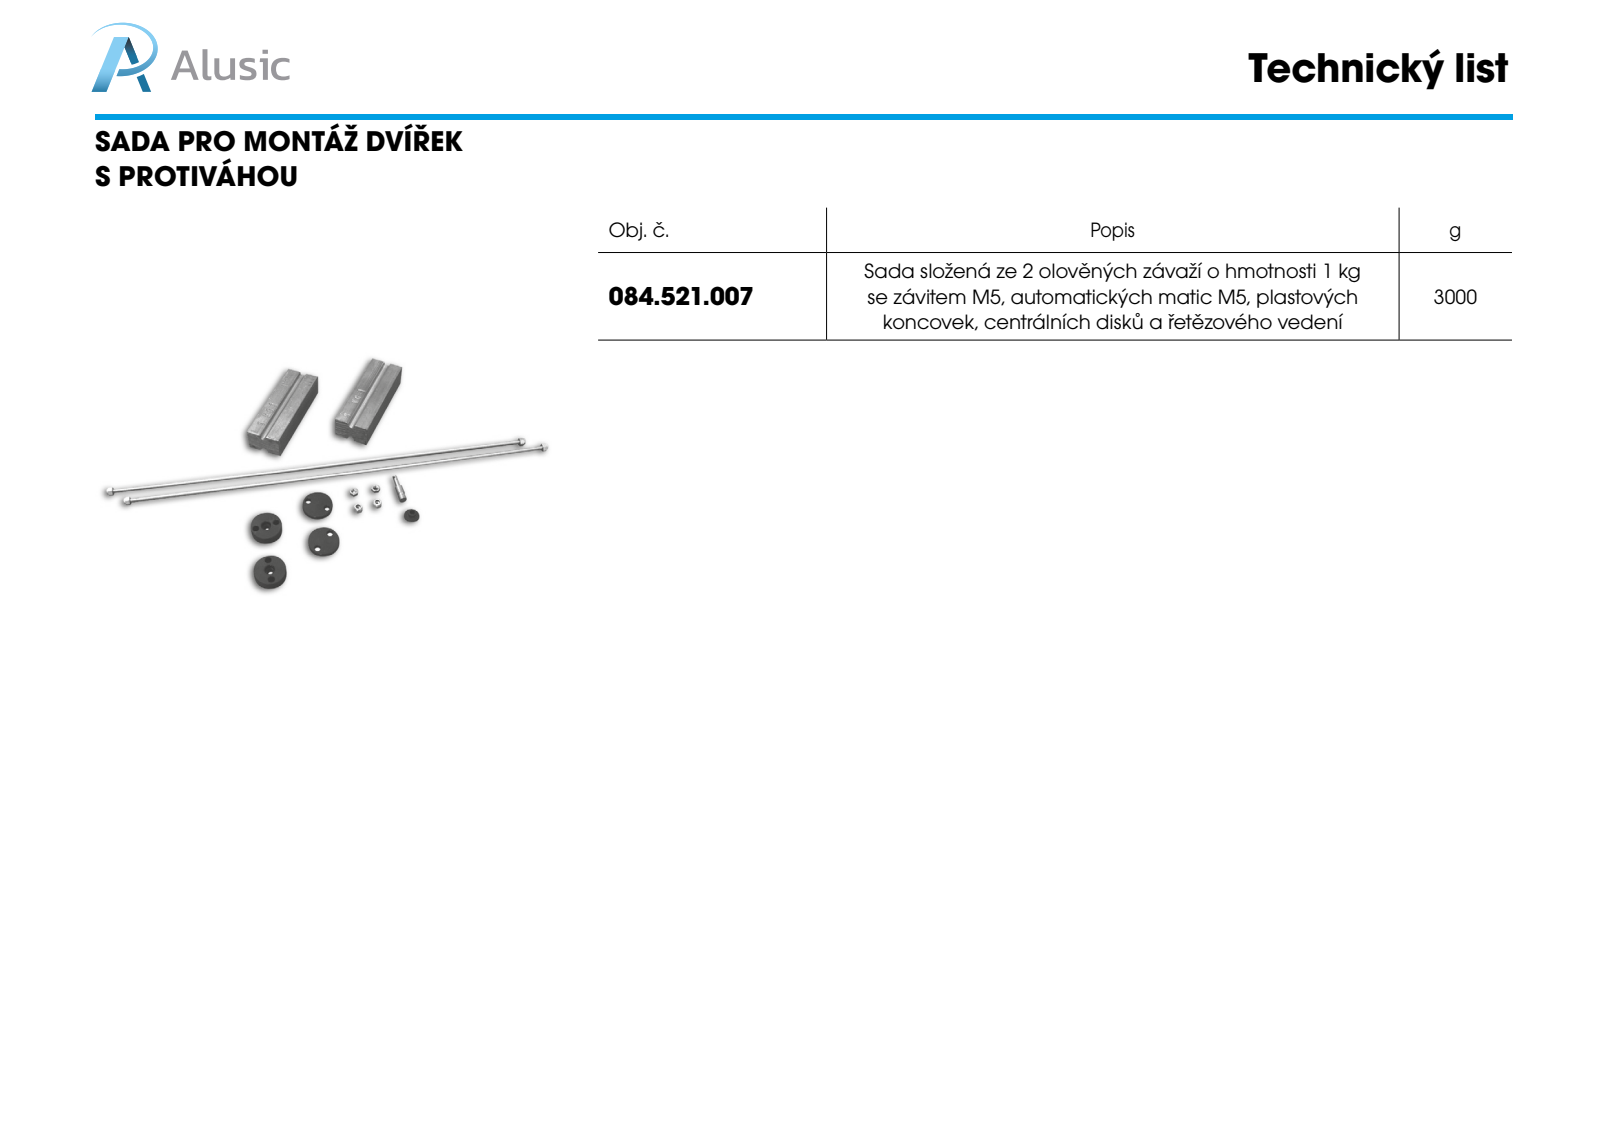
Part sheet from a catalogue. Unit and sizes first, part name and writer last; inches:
Units: inches
Overall size (bounding box): 19.783 × 1.457 × 1.142
Round holes (diameter × count): ⌀0.217 ×3, ⌀0.165 ×2, ⌀0.197 ×2, ⌀0.231 ×2, ⌀0.079 ×1, ⌀0.354 ×1
Round bosses / shafts (diameter × count): ⌀0.315 ×3, ⌀1.142 ×1, ⌀0.197 ×1, ⌀0.177 ×1
Partial cylindrical surfaces — rounded edges, fillets, slot ends (radius × count): R0.039 ×8, R0.118 ×2, R0.197 ×1
Main face-to-face distances: 0.984, 1.457, 4.469, 0.236, 4.705, 18.622, 0.61, 0.846, 8.937, 9.173
Hole centre spacings: 0.394, 0.787
Volume: 13.86 in³ · Surface area: 89.35 in²
Bodies: 12 solids, 404 faces (73 planar, 147 cylindrical, 184 other)
Part name (STEP PRODUCT): 084.521.007; ISO 7040-M5-C_ISO 7040-M5-C; 084.521.112; 084.521.005 (+3 more)
STEP written by: SolidWorks 2016 (CONFIG_CONTROL_DESIGN)
